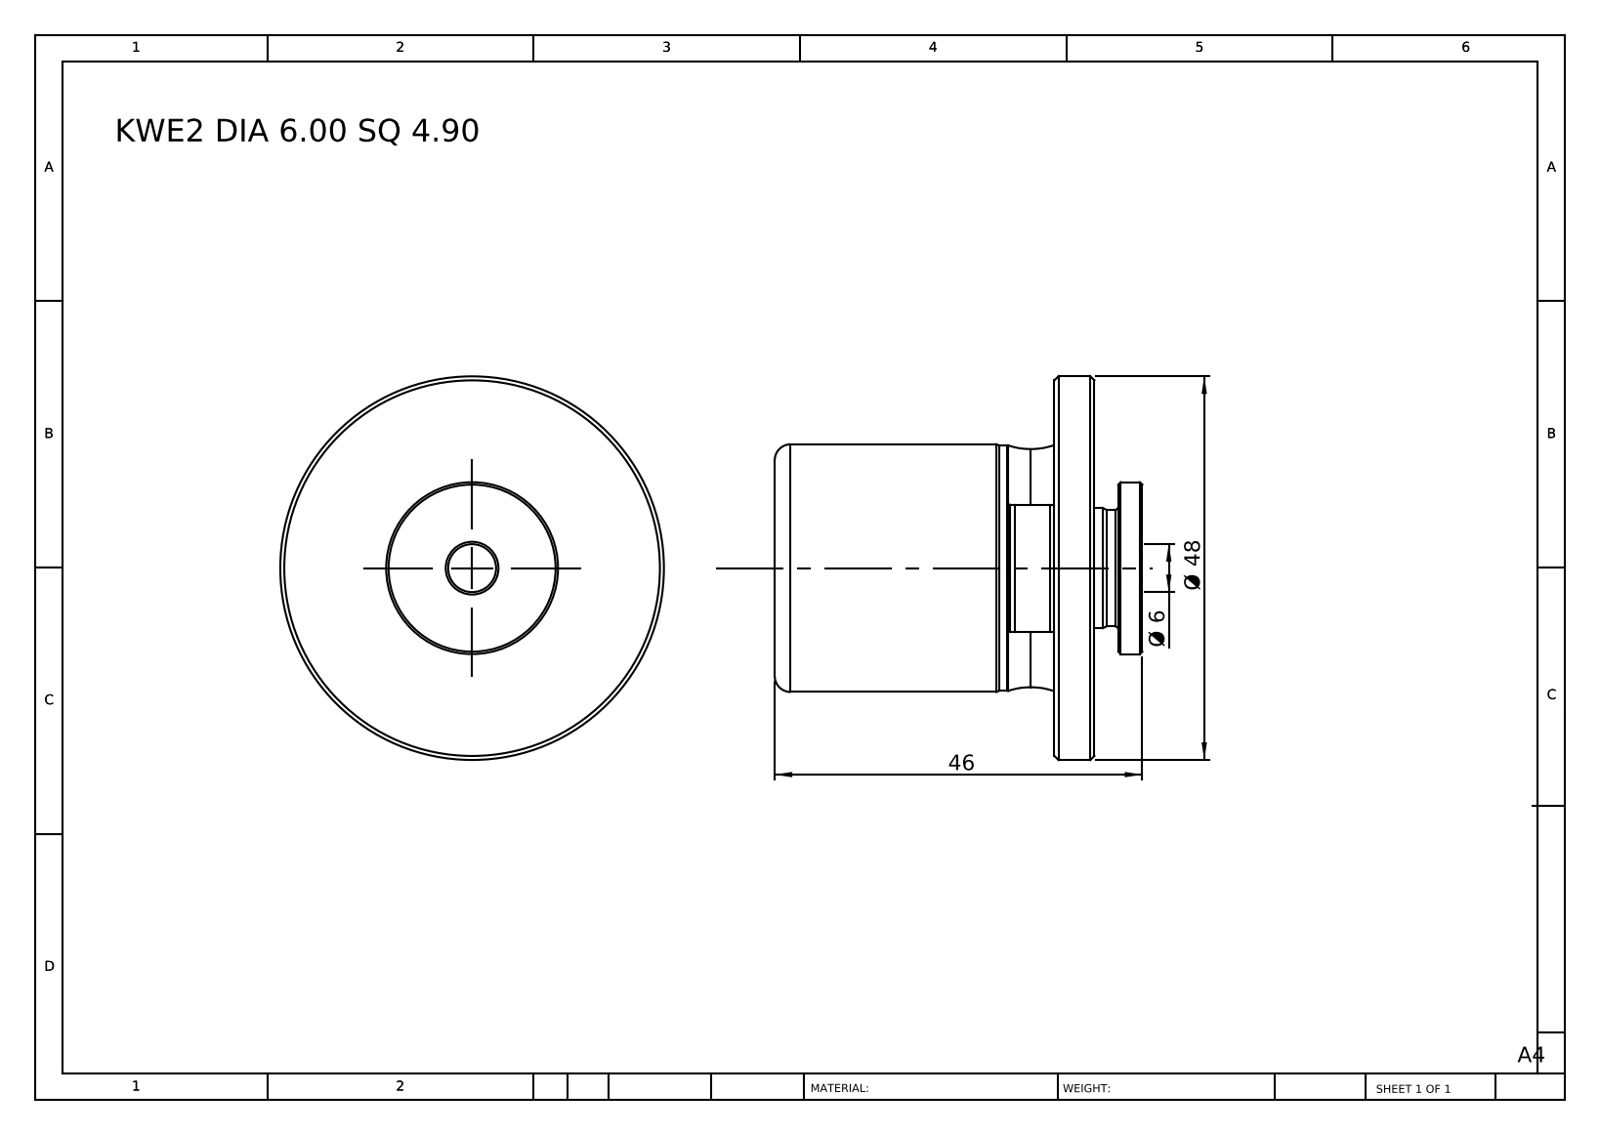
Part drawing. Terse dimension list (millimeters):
name: KWE2 DIA 6.00 SQ 4.90
written by: SolidWorks 2014 (CONFIG_CONTROL_DESIGN)
unit: mm
bodies: 1 solid, 61 faces (12 planar, 17 cylindrical, 32 other)
size: 48 × 48 × 46
volume: 36 990 mm³; area: 8 802 mm²
holes: 1× ⌀6
bosses: 1× ⌀48, 1× ⌀31, 1× ⌀30.7, 1× ⌀21.5, 1× ⌀15, 1× ⌀14.6
rounds: 1× R19.9
face distances: 5, 35, 40, 3, 46, 11, 6, 43, 8, 29.5
